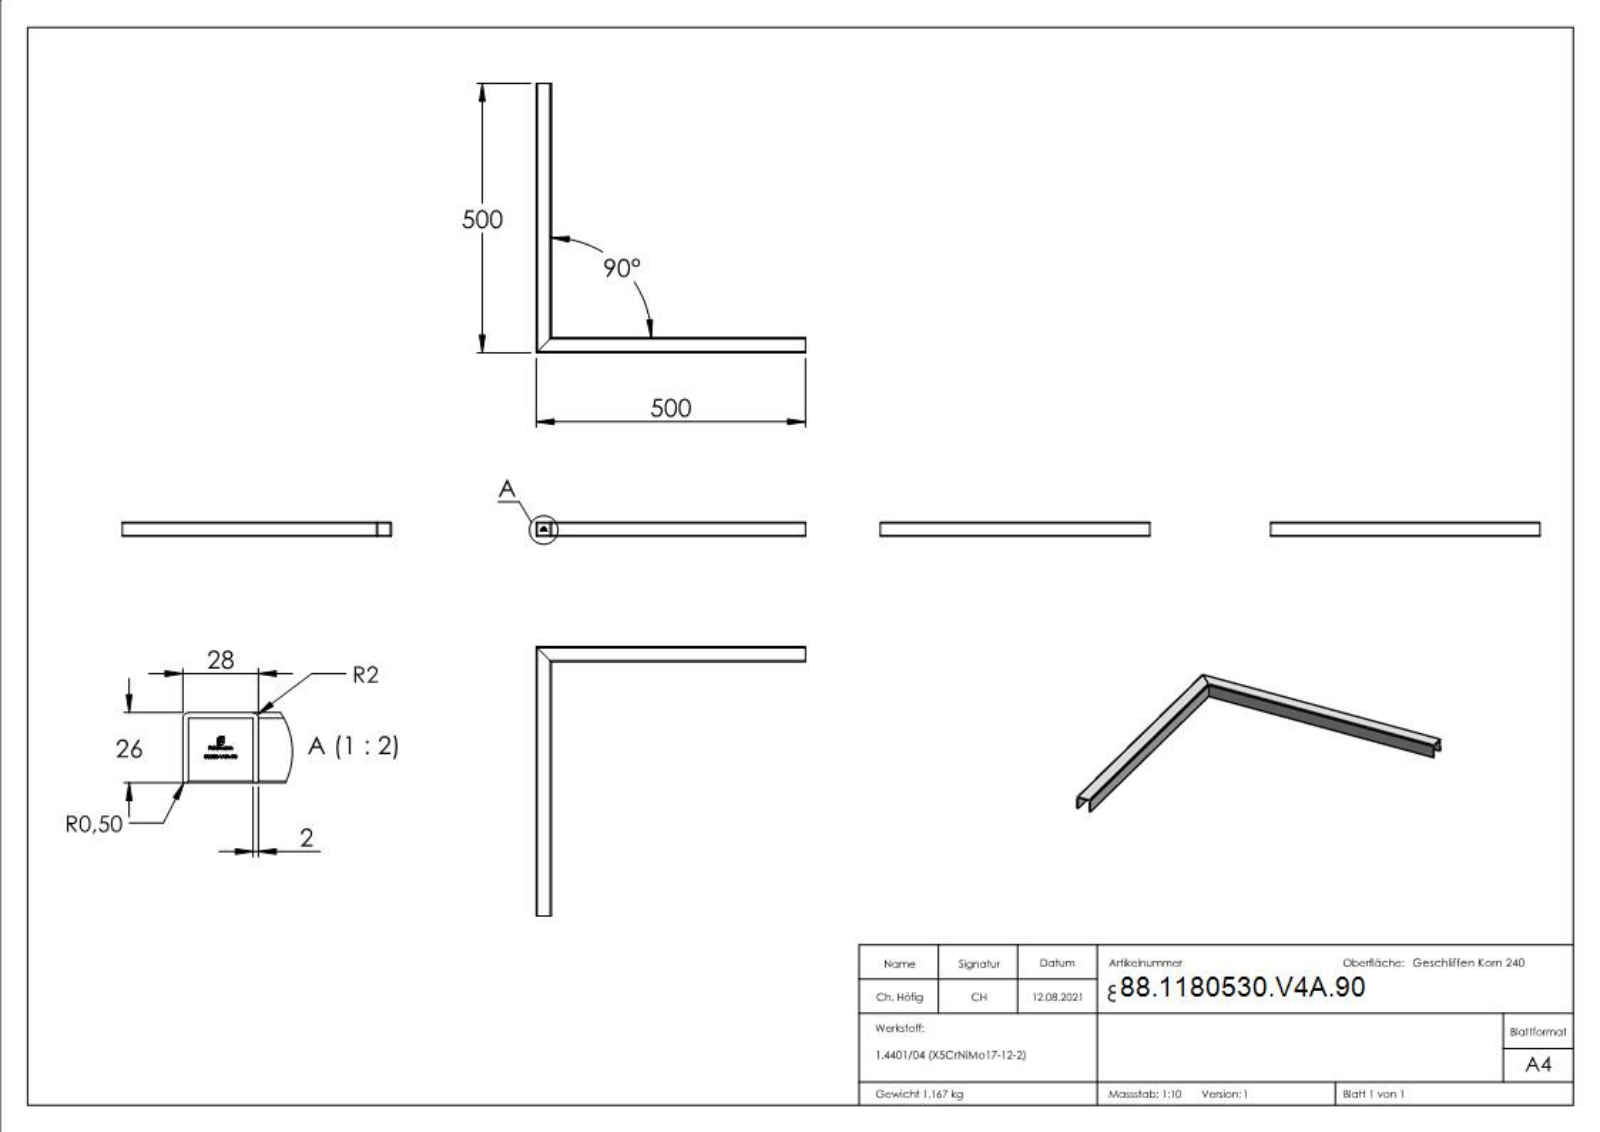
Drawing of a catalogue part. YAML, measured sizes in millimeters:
part_name: "80530-V4A-90"
step_written_by: "SolidWorks 2018 (CONFIG_CONTROL_DESIGN)"
units: millimeters
bodies: {solids: 1, faces: 332, planar: 177, cylindrical: 12, other: 143}
overall_size: [500, 500, 26]
volume: 145865
surface_area: 149443
partial_cylinders:
  - {radius: 0.5, count: 8}
  - {radius: 2, count: 4}
face_to_face_distances: [2, 26, 24, 28, 500, 498, 474, 472, 1.9, 24.1]
